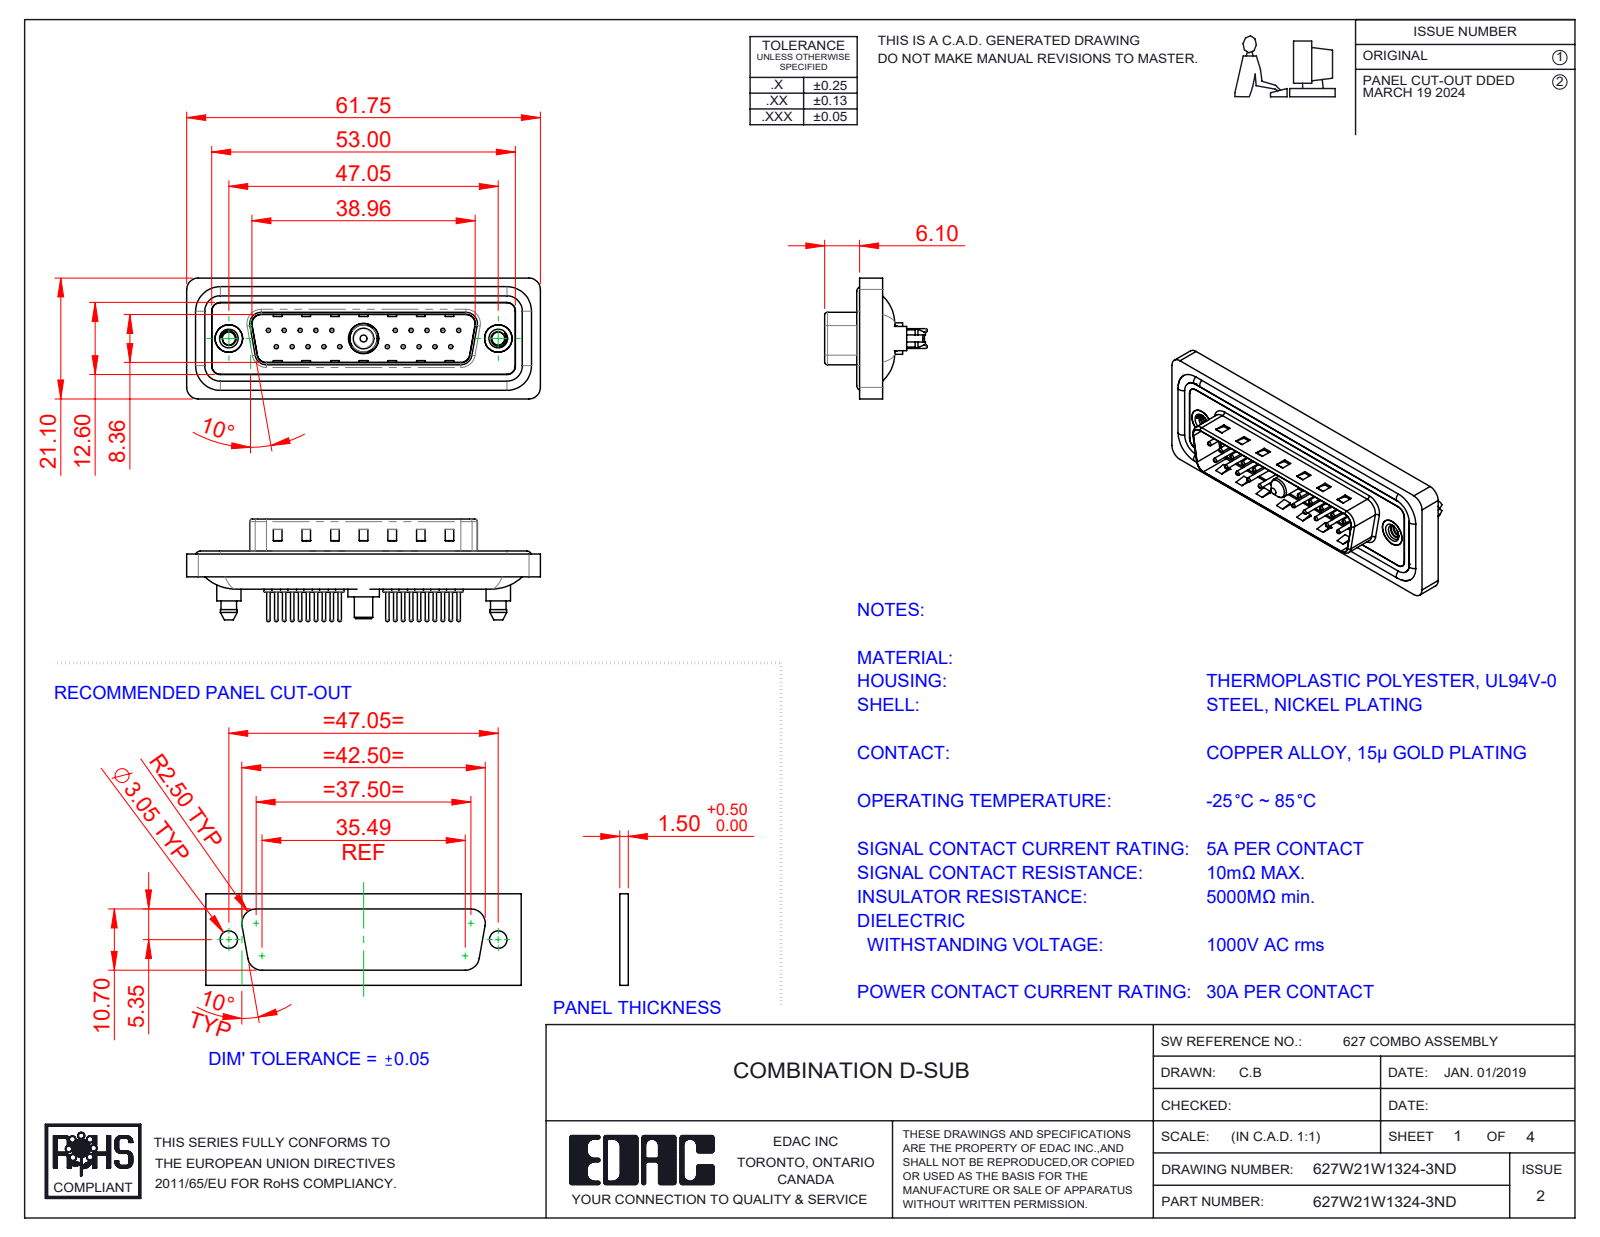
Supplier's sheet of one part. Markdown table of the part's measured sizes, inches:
| quantity | value |
| --- | --- |
| part name | 627Combo Contact Row 1_24; Power Pin_30A S; 627Combo Shell Front_25 Contacts; 627Combo Waterproof Housing_25 Contacts (+6 more) |
| STEP written by | SolidWorks 2023 (CONFIG_CONTROL_DESIGN) |
| units | inches |
| bodies | 29 solids, 1320 faces (375 planar, 527 cylindrical, 418 other) |
| overall size | 2.431 × 0.831 × 0.705 |
| volume | 0.448 in³ |
| surface area | 19.06 in² |
| round holes (diameter × count) | 0.03 × 20, 0.063 × 20, 0.079 × 20, 0.089 × 2, 0.157 × 2, 0.189 × 2, 0.197 × 2, 0.191 × 1, 0.209 × 1 |
| round bosses / shafts (diameter × count) | 0.059 × 20, 0.024 × 20, 0.063 × 4, 0.213 × 2, 0.193 × 2, 0.167 × 2, 0.217 × 1, 0.205 × 1 |
| partial cylindrical surfaces (radius × count) | 0.059 × 24, 0.079 × 18, 0.063 × 10, 0.02 × 8, 0.01 × 4, 0.024 × 4, 0.026 × 4, 0.035 × 4 |
| main face-to-face distances | 0.016, 0.059, 0.043, 0.063, 0.02, 0.122, 0.114, 0.161, 0.032, 0.377 |
| hole center spacings | 0.124, 0.109, 0.218, 0.327, 0.198, 0.763, 0.826, 0.872 |
